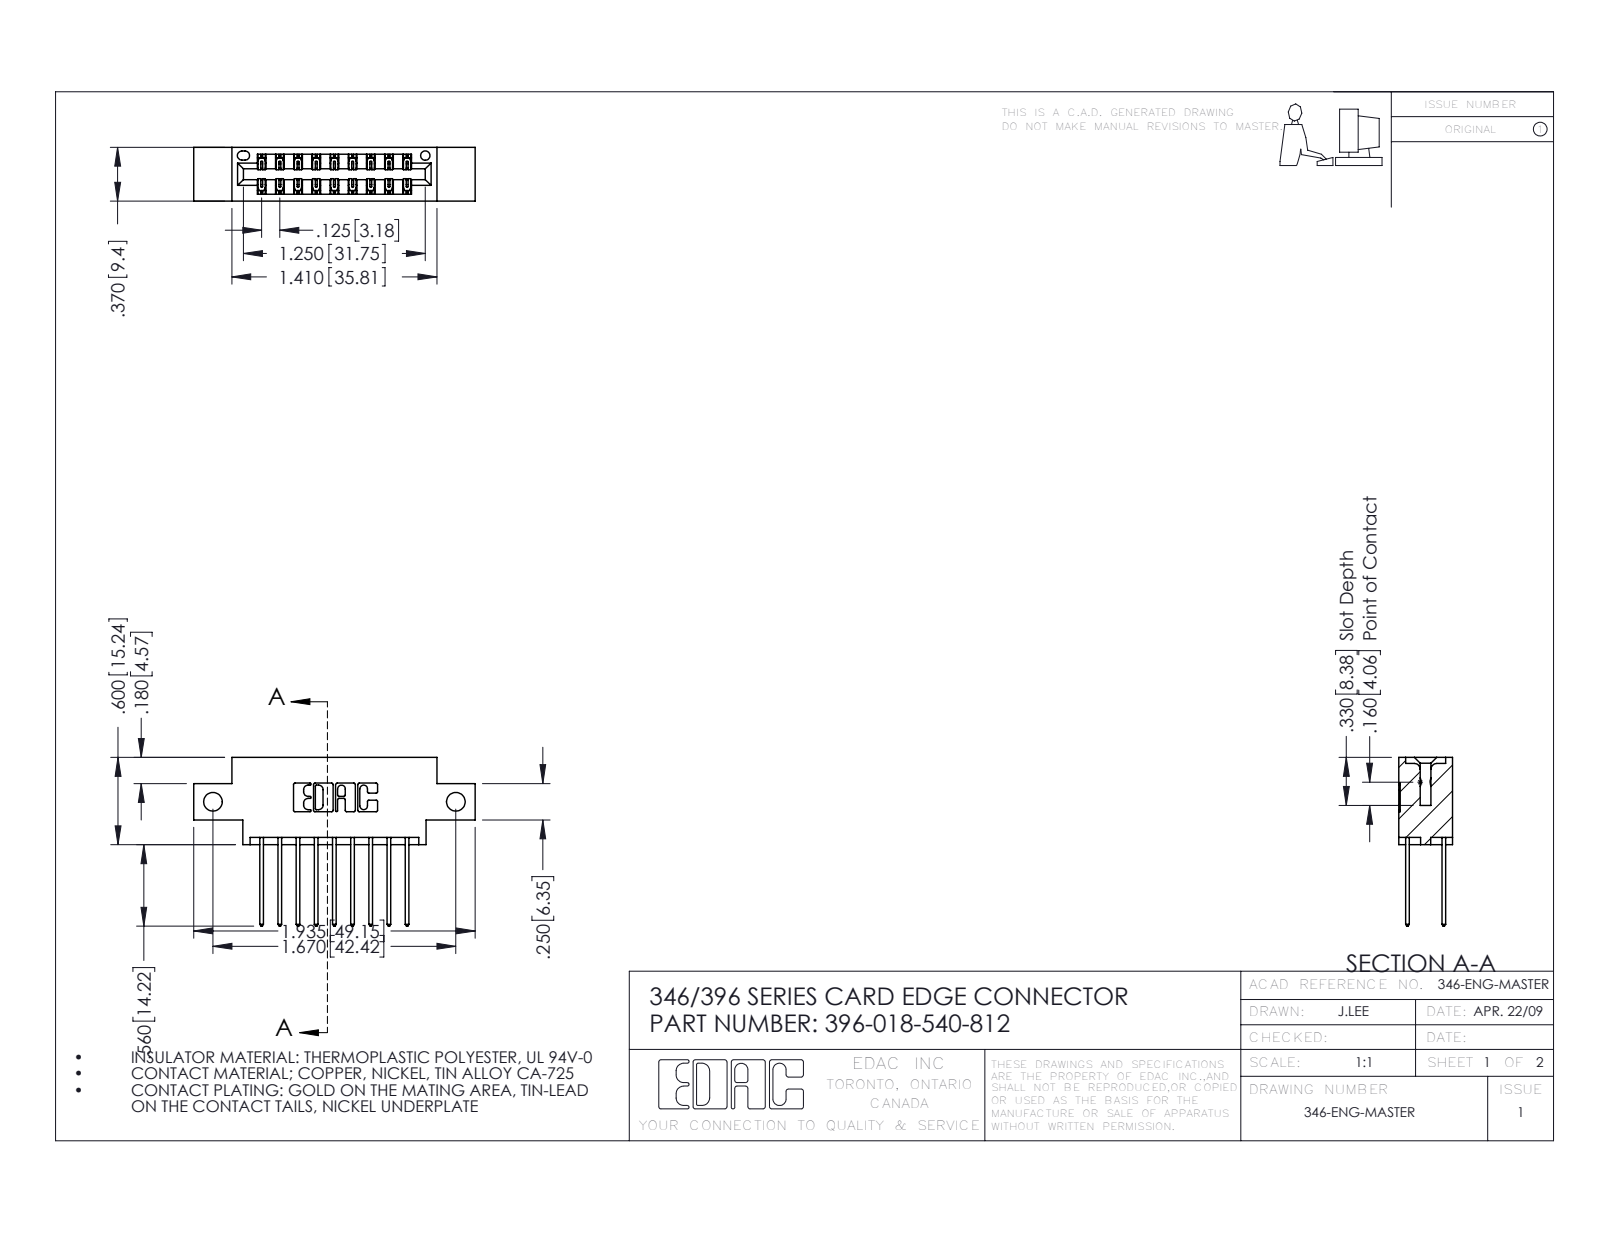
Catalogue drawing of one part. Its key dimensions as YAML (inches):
part_name: "346 Part_0.170 Offset - Side Mount; 396-018-540-812; 345-292-001_345-293-140"
step_written_by: "SolidWorks 2016 (CONFIG_CONTROL_DESIGN)"
units: inches
bodies: {solids: 19, faces: 1062, planar: 710, cylindrical: 352, other: 0}
overall_size: [1.935, 1.16, 0.37]
volume: 0.266
surface_area: 9.057
round_holes:
  - {diameter: 0.128, count: 2}
  - {diameter: 0.064, count: 1}
partial_cylinders:
  - {radius: 0.006, count: 27}
  - {radius: 0.01, count: 22}
  - {radius: 0.01, count: 18}
  - {radius: 0.007, count: 6}
  - {radius: 0.031, count: 6}
  - {radius: 0.026, count: 3}
  - {radius: 0.014, count: 2}
  - {radius: 0.022, count: 2}
face_to_face_distances: [0.25, 0.048, 0.322, 0.37, 0.072, 0.298, 0.025, 0.275, 0.225, 0.148]
hole_center_spacings: [1.67]
